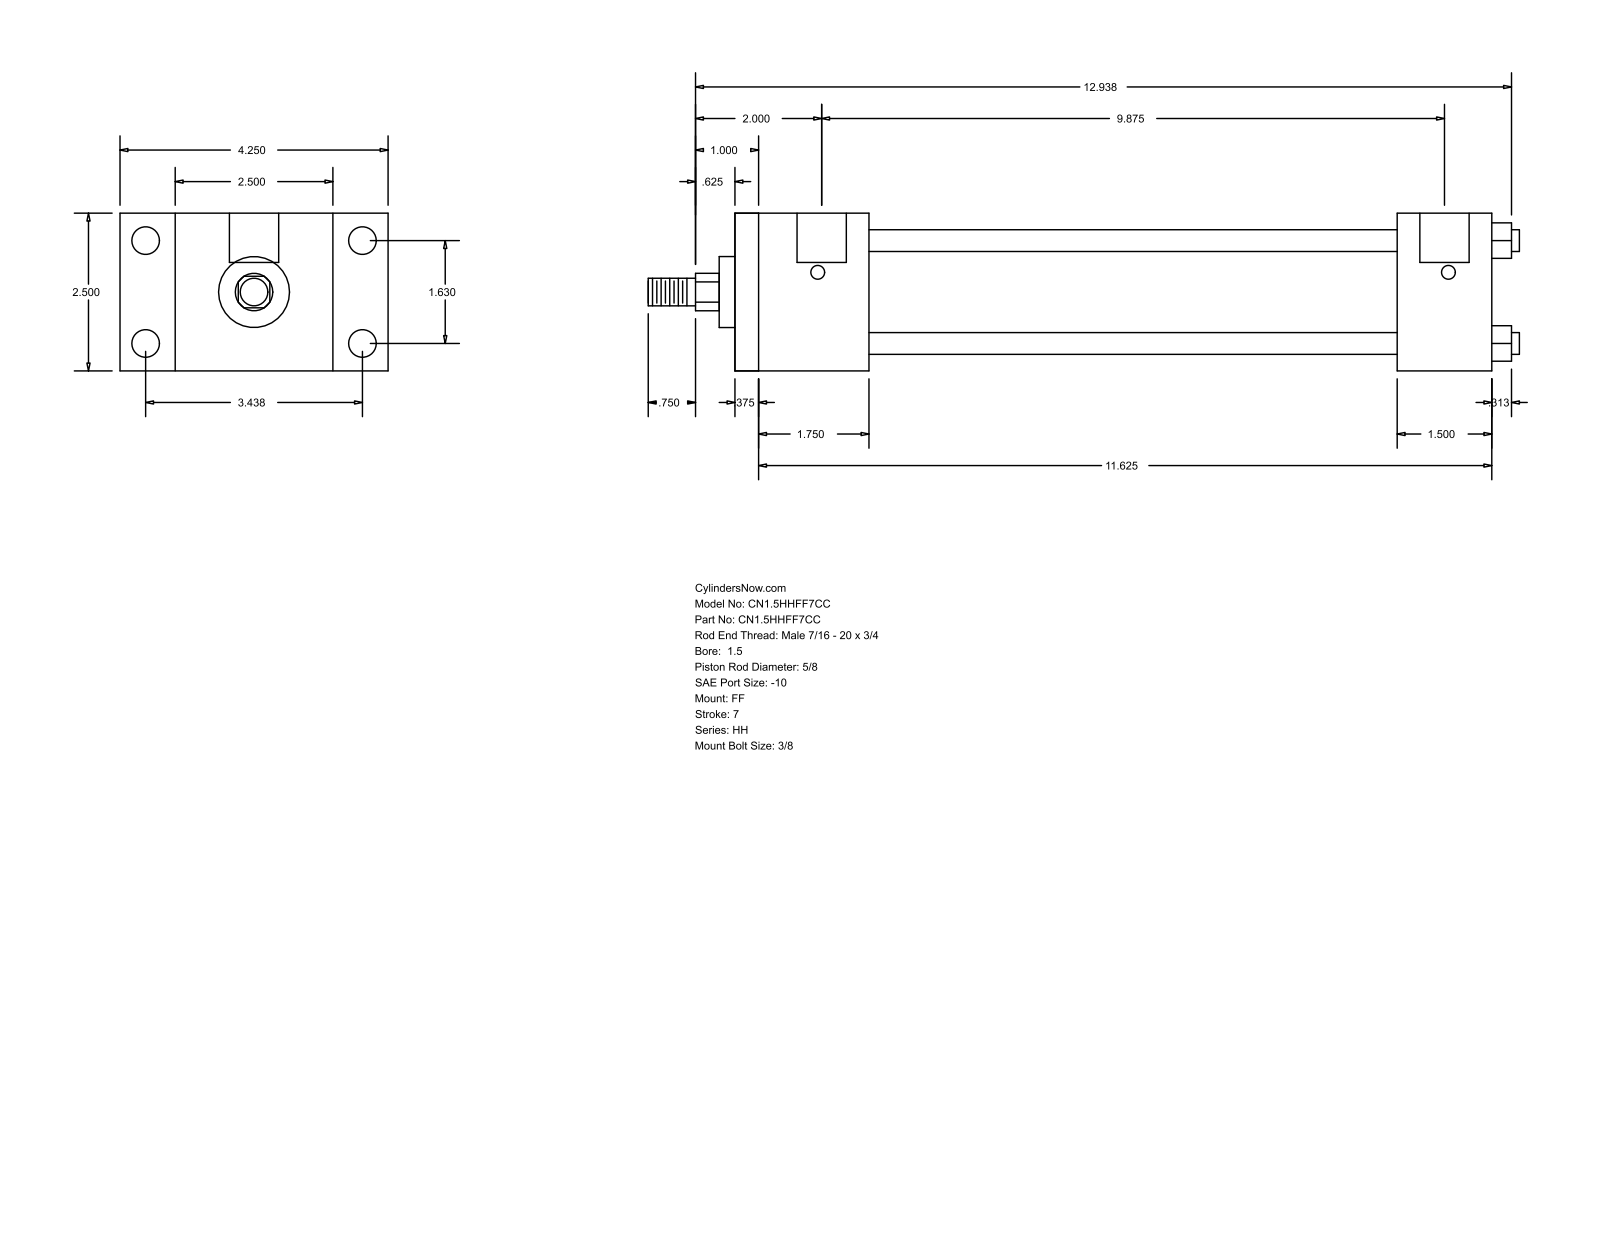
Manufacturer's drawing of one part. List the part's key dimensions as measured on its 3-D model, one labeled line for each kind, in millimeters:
Part name (STEP PRODUCT): HH_FF__0150_0.625
STEP written by: GSSL Pune (CONFIG_CONTROL_DESIGN)
Units: millimetres
Bodies: 0 solids, 92 faces (64 planar, 28 cylindrical, 0 other)
Overall size (bounding box): 350.84 × 107.95 × 63.5
Round holes (diameter × count): ⌀5.56 ×4, ⌀11.13 ×4, ⌀19.84 ×2
Round bosses / shafts (diameter × count): ⌀8.76 ×4, ⌀44.45 ×1, ⌀28.57 ×1, ⌀15.88 ×1, ⌀11.11 ×1
Partial cylindrical surfaces — rounded edges, fillets, slot ends (radius × count): R7.54 ×1
Main face-to-face distances: 63.5, 304.8, 9.52, 295.28, 44.45, 53.97, 250.83, 266.69, 257.17, 212.72
Hole centre spacings: 1.59, 41.4, 87.32, 96.64, 252.41, 254, 250.82
